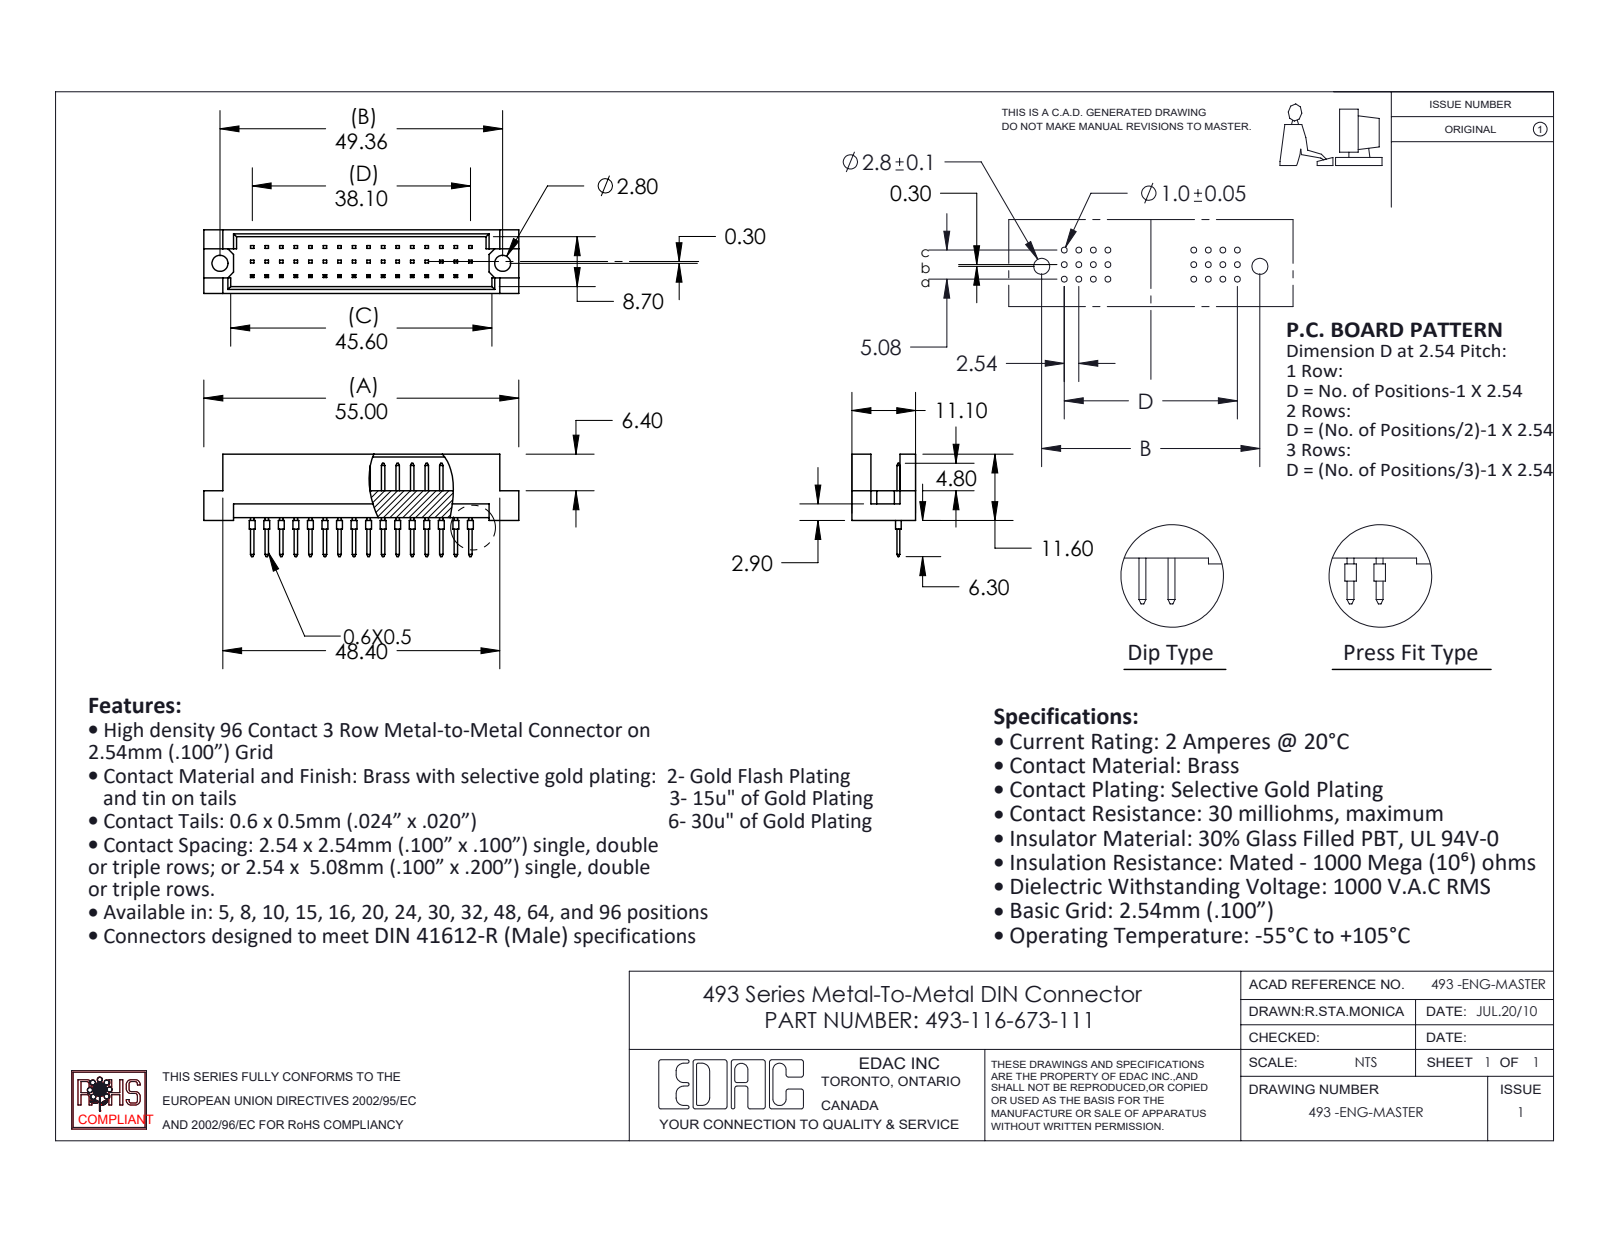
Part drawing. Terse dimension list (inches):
name: 493-290_73; 493 Part_48; 493-116-673-111
written by: SolidWorks 2020 (CONFIG_CONTROL_DESIGN)
unit: in
bodies: 17 solids, 596 faces (560 planar, 36 cylindrical, 0 other)
size: 2.165 × 0.705 × 0.437
volume: 0.205 in³; area: 6.761 in²
holes: 2× ⌀0.11
bosses: 16× ⌀0.039
face distances: 0.047, 0.39, 0.437, 0.343, 0.02, 0.185, 0.1, 0.2, 0.109, 0.328
hole spacings: 1.943
